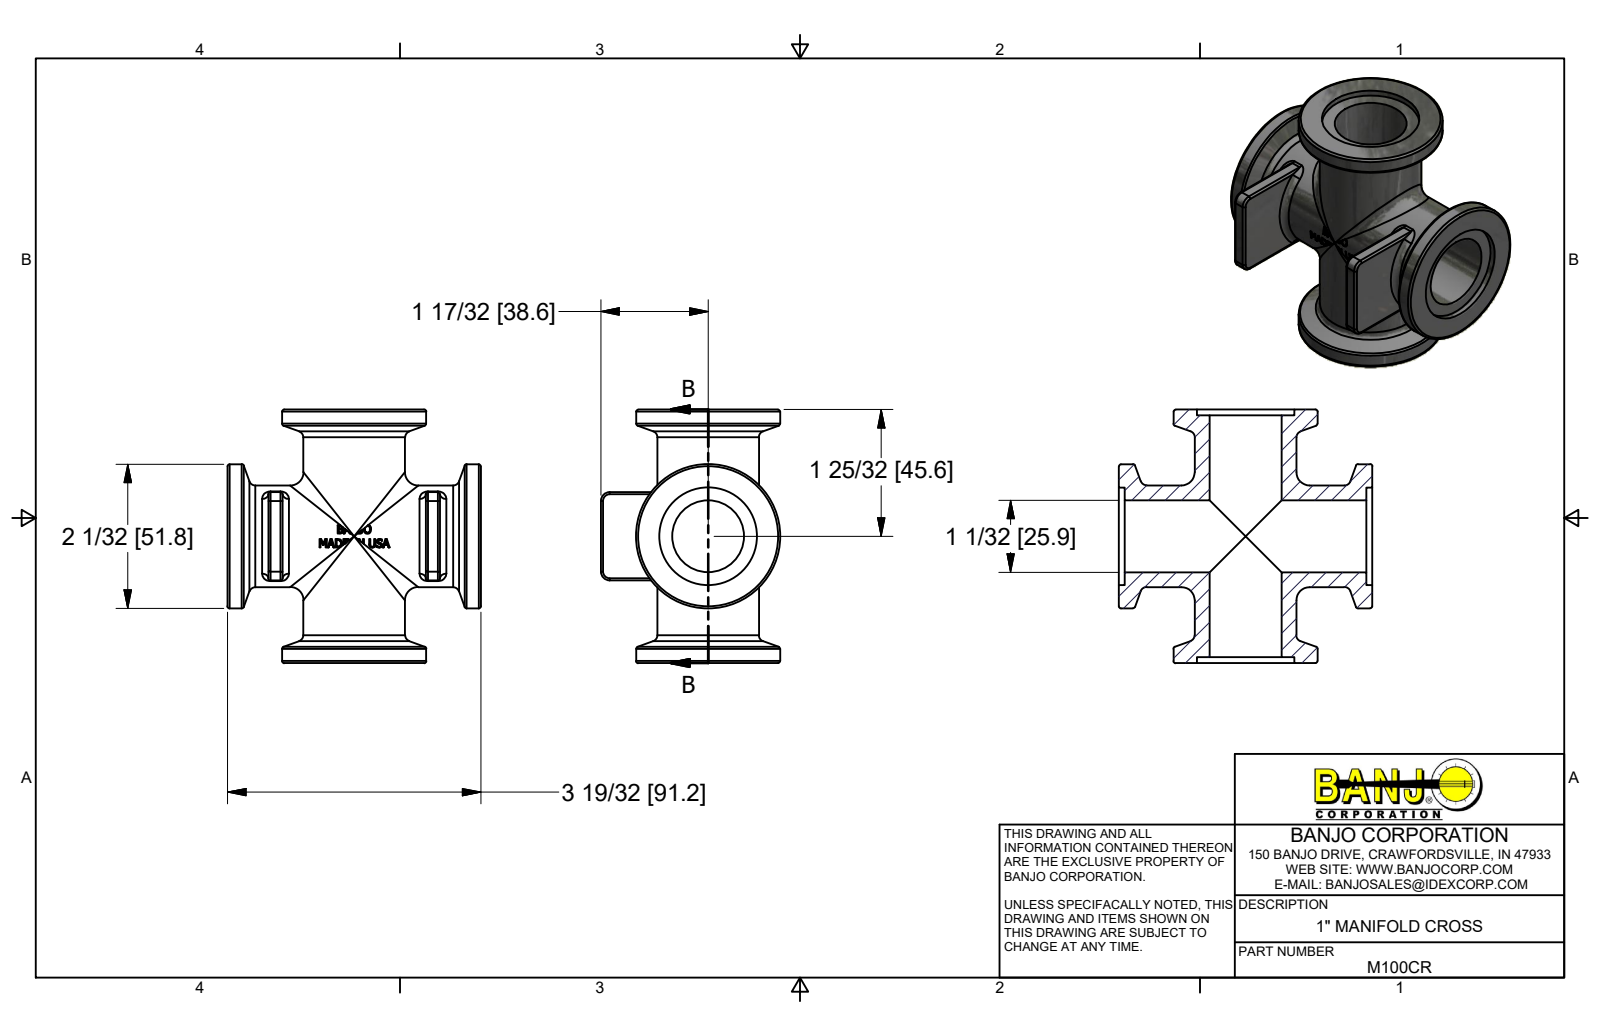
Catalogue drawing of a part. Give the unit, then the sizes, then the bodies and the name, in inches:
Units: inches
Overall size (bounding box): 3.59 × 3.59 × 2.54
Round holes (diameter × count): ⌀1.02 ×2, ⌀1.38 ×2
Round bosses / shafts (diameter × count): ⌀2.04 ×2, ⌀1.44 ×2
Partial cylindrical surfaces — rounded edges, fillets, slot ends (radius × count): R0.03 ×12, R0.09 ×2, R0.125 ×2, R0.7 ×2
Main face-to-face distances: 3.59, 2.23, 0.2, 0.084, 3.506, 3.422, 3.506, 0.084, 0.496, 0.696
Volume: 6.597 in³ · Surface area: 64.11 in²
Bodies: 1 solid, 434 faces (153 planar, 88 cylindrical, 193 other)
Part name (STEP PRODUCT): M100CR; M100CRU
STEP written by: Autodesk Inventor 2017 (AUTOMOTIVE_DESIGN)
